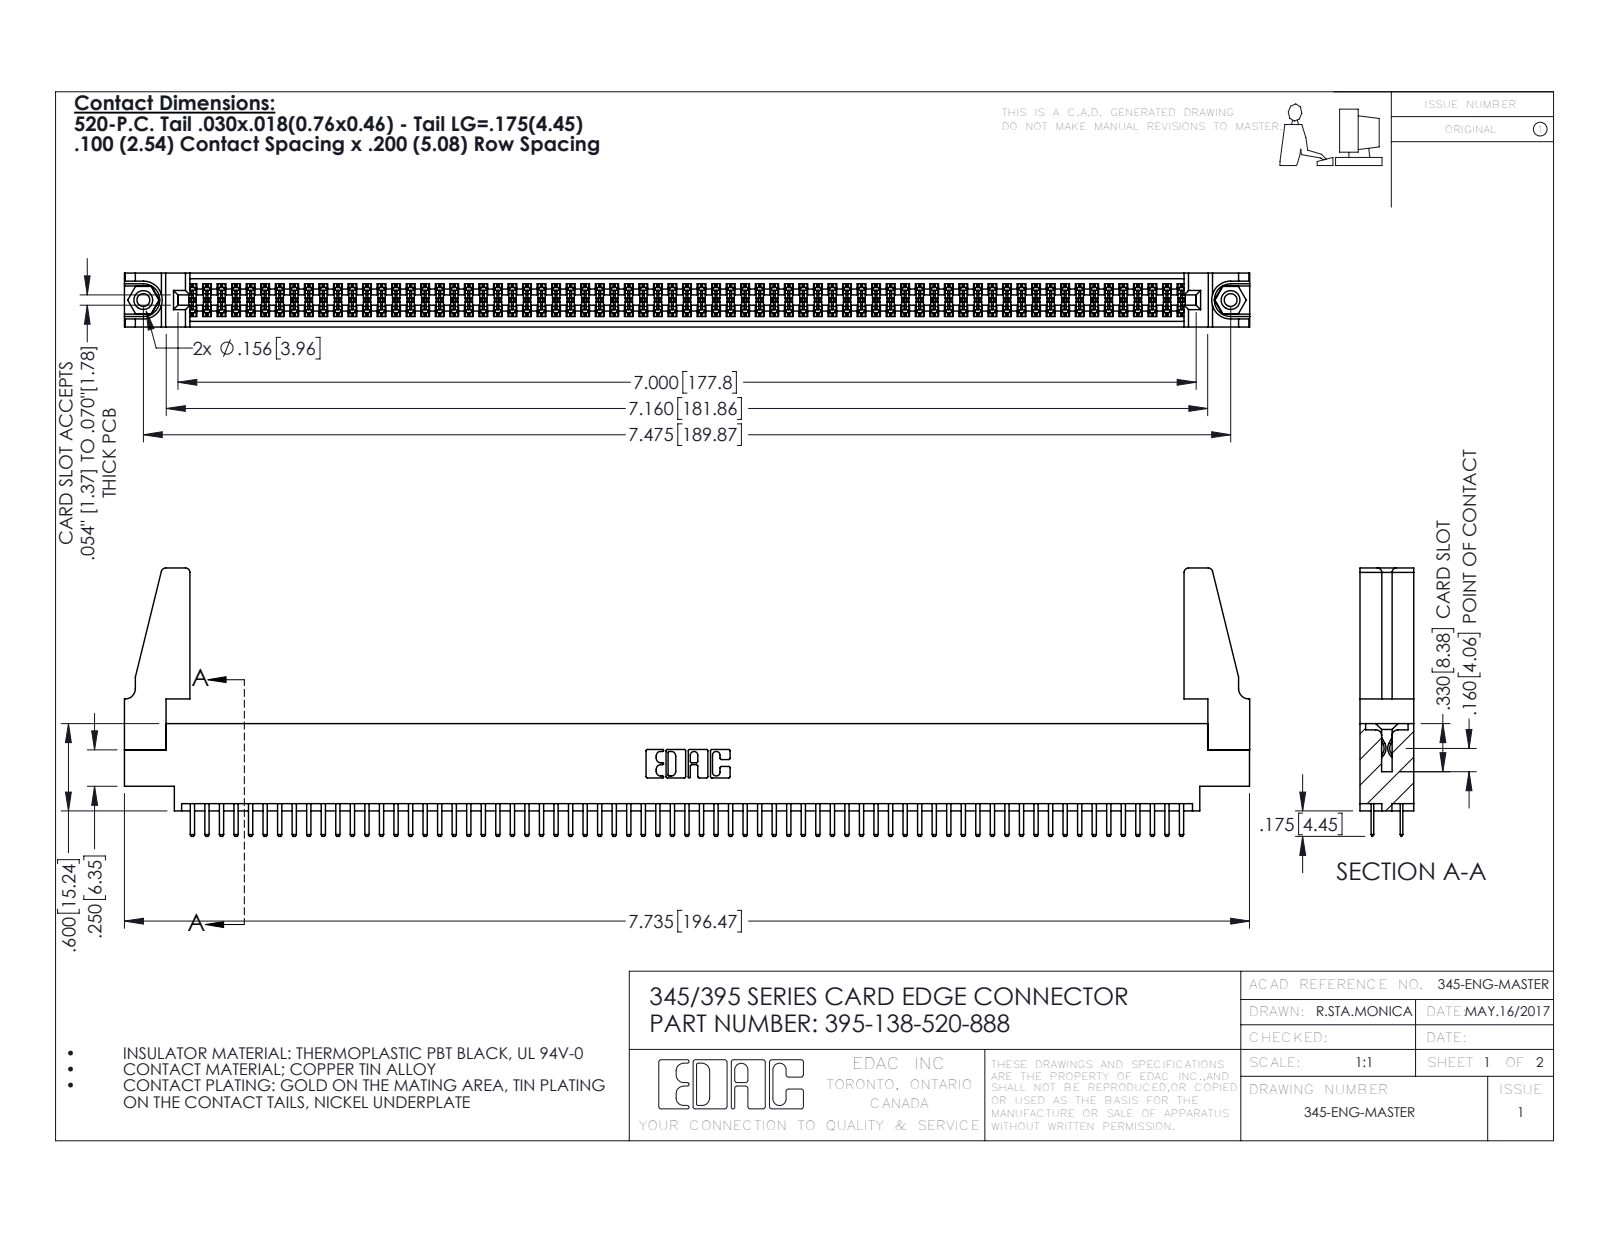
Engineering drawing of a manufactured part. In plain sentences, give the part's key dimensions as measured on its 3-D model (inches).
The part is named "345 Part_0.170 Offset - 0.156 Dia-TH; 345-250-001_345-250-001-102; 345-292-001_345-293-120; 395-138-520-888 (+1 more)". Its 3-D file was written by "SolidWorks 2016 (CONFIG_CONTROL_DESIGN)". It is 143 solids with 7706 faces: 4986 planar, 2704 cylindrical and 16 other. Overall it measures 7.736 by 1.845 by 0.37 inches. Its volume is 1.368 cubic inches and its surface area 49.58 square inches. Round holes: 2 of diameter 0.089, 2 of diameter 0.125, 2 of diameter 0.156, 1 of diameter 0.064. Round bosses or shafts: 2 of diameter 0.155. Partial cylindrical surfaces (rounded edges, fillets, slot ends): 207 of radius 0.006, 142 of radius 0.01, 22 of radius 0.01, 8 of radius 0.03, 6 of radius 0.007, 6 of radius 0.031, 3 of radius 0.026, 2 of radius 0.014. The main face-to-face distances are 0.072, 0.298, 0.37, 0.2, 0.098, 0.272, 0.025, 0.225, 0.022, 0.072. The hole center spacings are 0.27, 7.239, 7.475.
